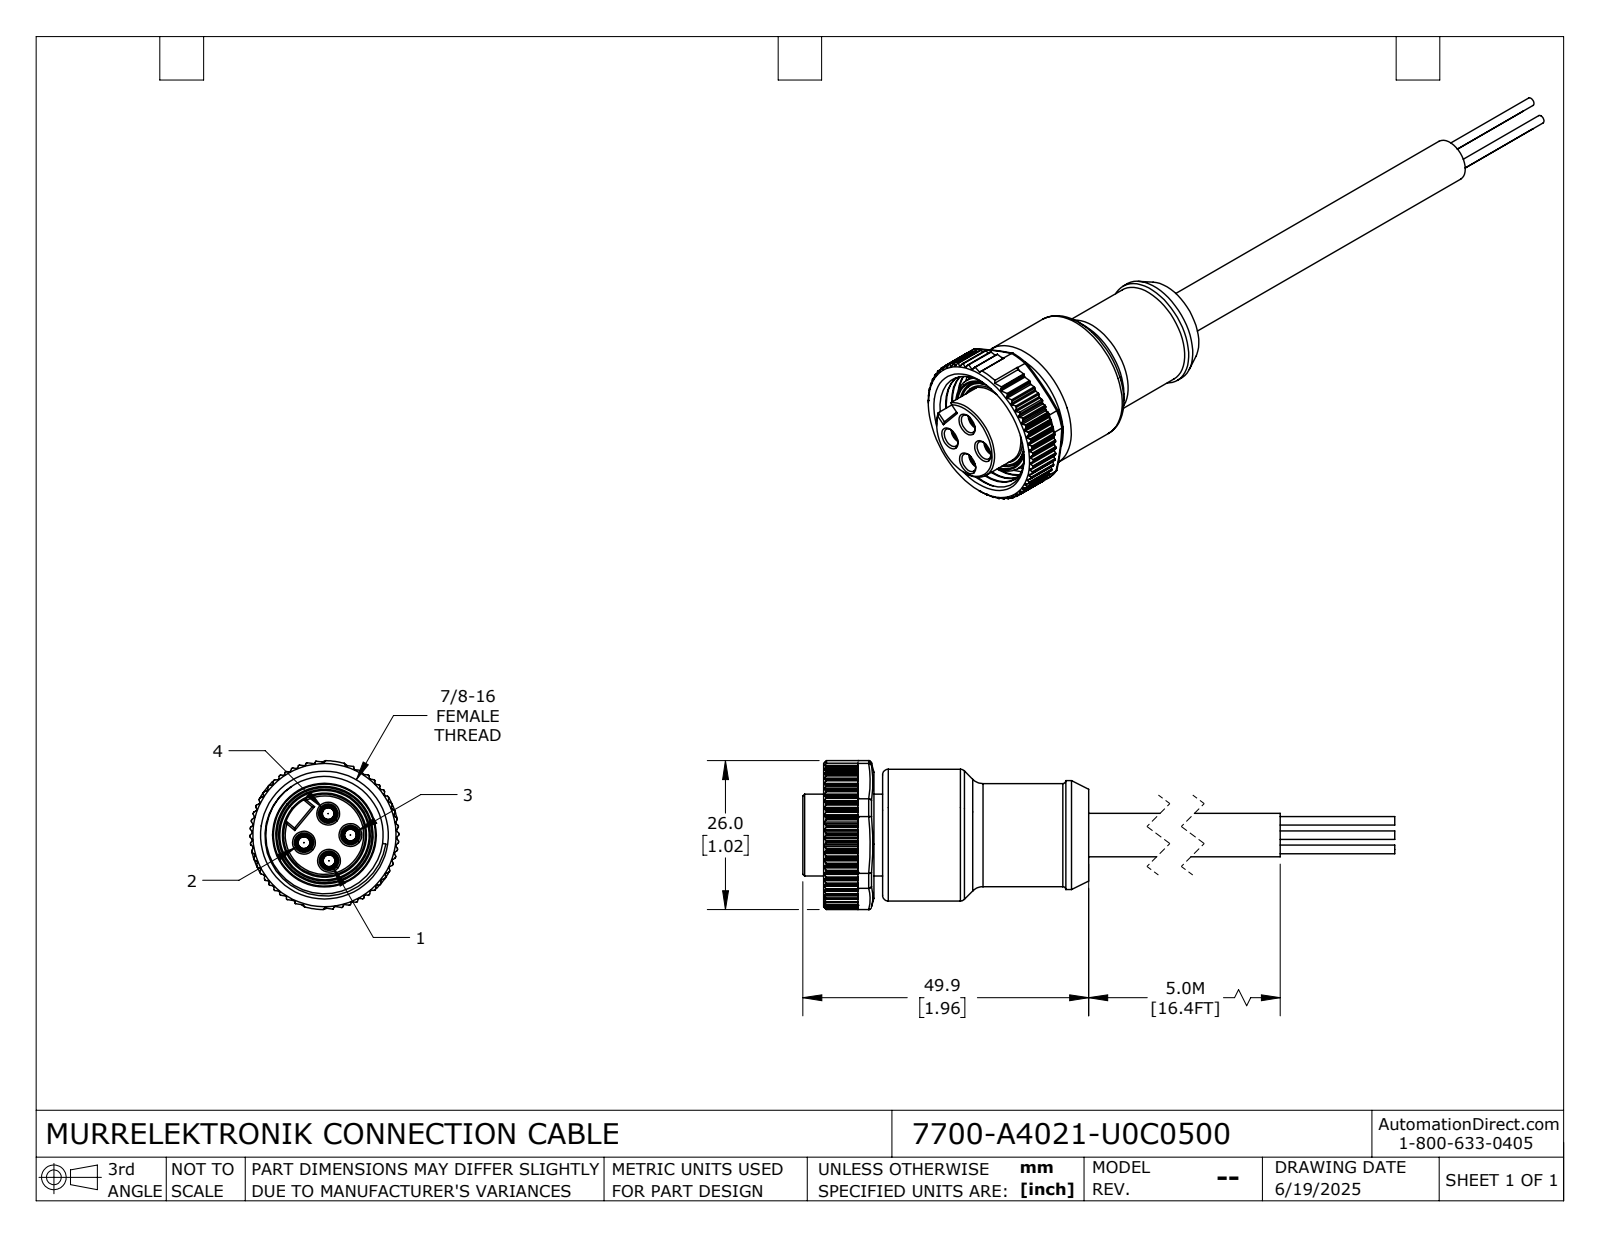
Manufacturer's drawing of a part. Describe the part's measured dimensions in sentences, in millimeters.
The part is named "7700-A4021-U0C0500". Its 3-D file was written by "SolidWorks 2024 (CONFIG_CONTROL_DESIGN)". It is 1 solid with 674 faces: 296 planar, 293 cylindrical and 85 other. Overall it measures 139.9 by 26 by 26 millimeters. Its volume is 18 784 cubic millimeters and its surface area 8 325 square millimeters. Round holes: 4 of diameter 2.05, 4 of diameter 3, 4 of diameter 3.4, 1 of diameter 15.5, 1 of diameter 15.6, 1 of diameter 20.5, 1 of diameter 22.23. Round bosses or shafts: 4 of diameter 1.5, 1 of diameter 23, 1 of diameter 19, 1 of diameter 18.1, 1 of diameter 18, 1 of diameter 17.8, 1 of diameter 14.3, 1 of diameter 7.6. Partial cylindrical surfaces (rounded edges, fillets, slot ends): 126 of radius 0.2, 16 of radius 0.3, 4 of radius 0.1, 4 of radius 0.73, 1 of radius 13. The main face-to-face distances are 1.5, 37.5, 36, 3.6, 8.8, 10.3, 46.3, 12.4, 13.9, 49.9. The hole center spacings are 3.81, 4.54, 8.22, 5.39, 5.4, 5.84, 6.6.
